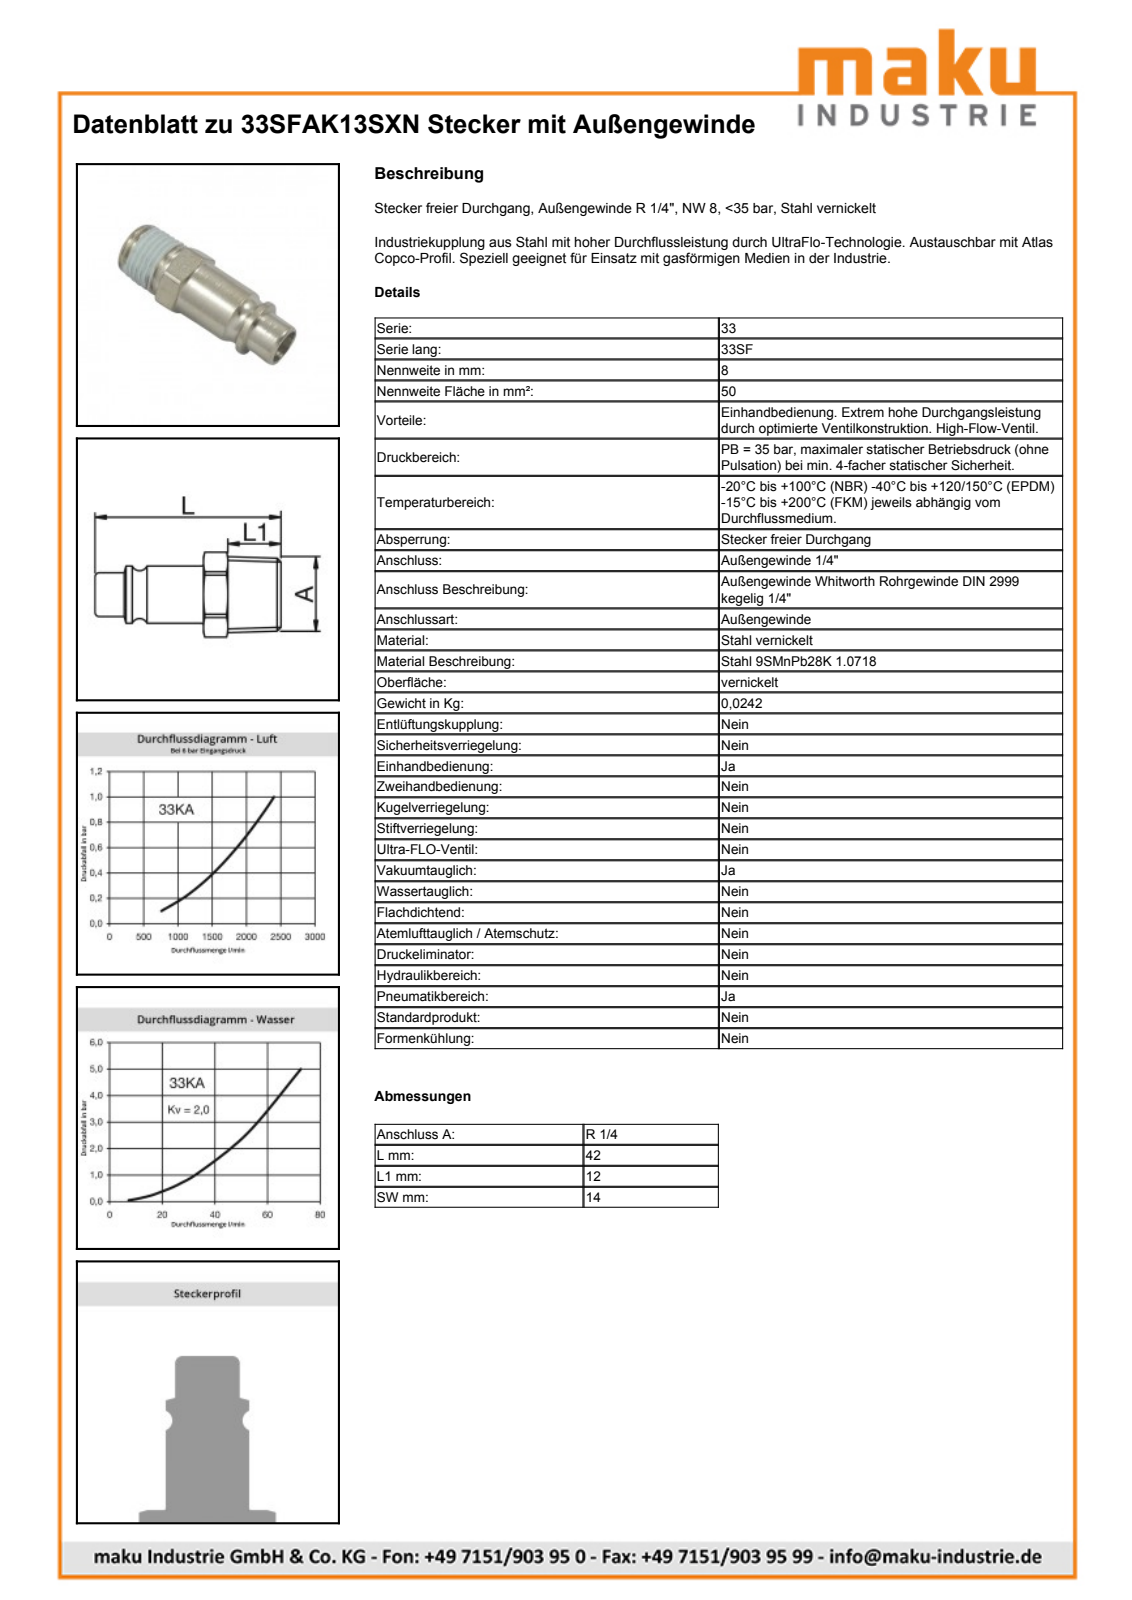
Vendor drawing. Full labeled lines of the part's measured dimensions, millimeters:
Part name (STEP PRODUCT): D104124
STEP written by: Autodesk Inventor 2011 (AUTOMOTIVE_DESIGN)
Units: millimetres
Bodies: 1 solid, 39 faces (9 planar, 10 cylindrical, 20 other)
Overall size (bounding box): 42 × 15.8 × 14
Volume: 3 266 mm³ · Surface area: 2 885 mm²
Round holes (diameter × count): ⌀7.8 ×1
Round bosses / shafts (diameter × count): ⌀12.9 ×1, ⌀9.9 ×1
Partial cylindrical surfaces — rounded edges, fillets, slot ends (radius × count): R7.9 ×1
Main face-to-face distances: 14, 17.5, 24.5, 42
